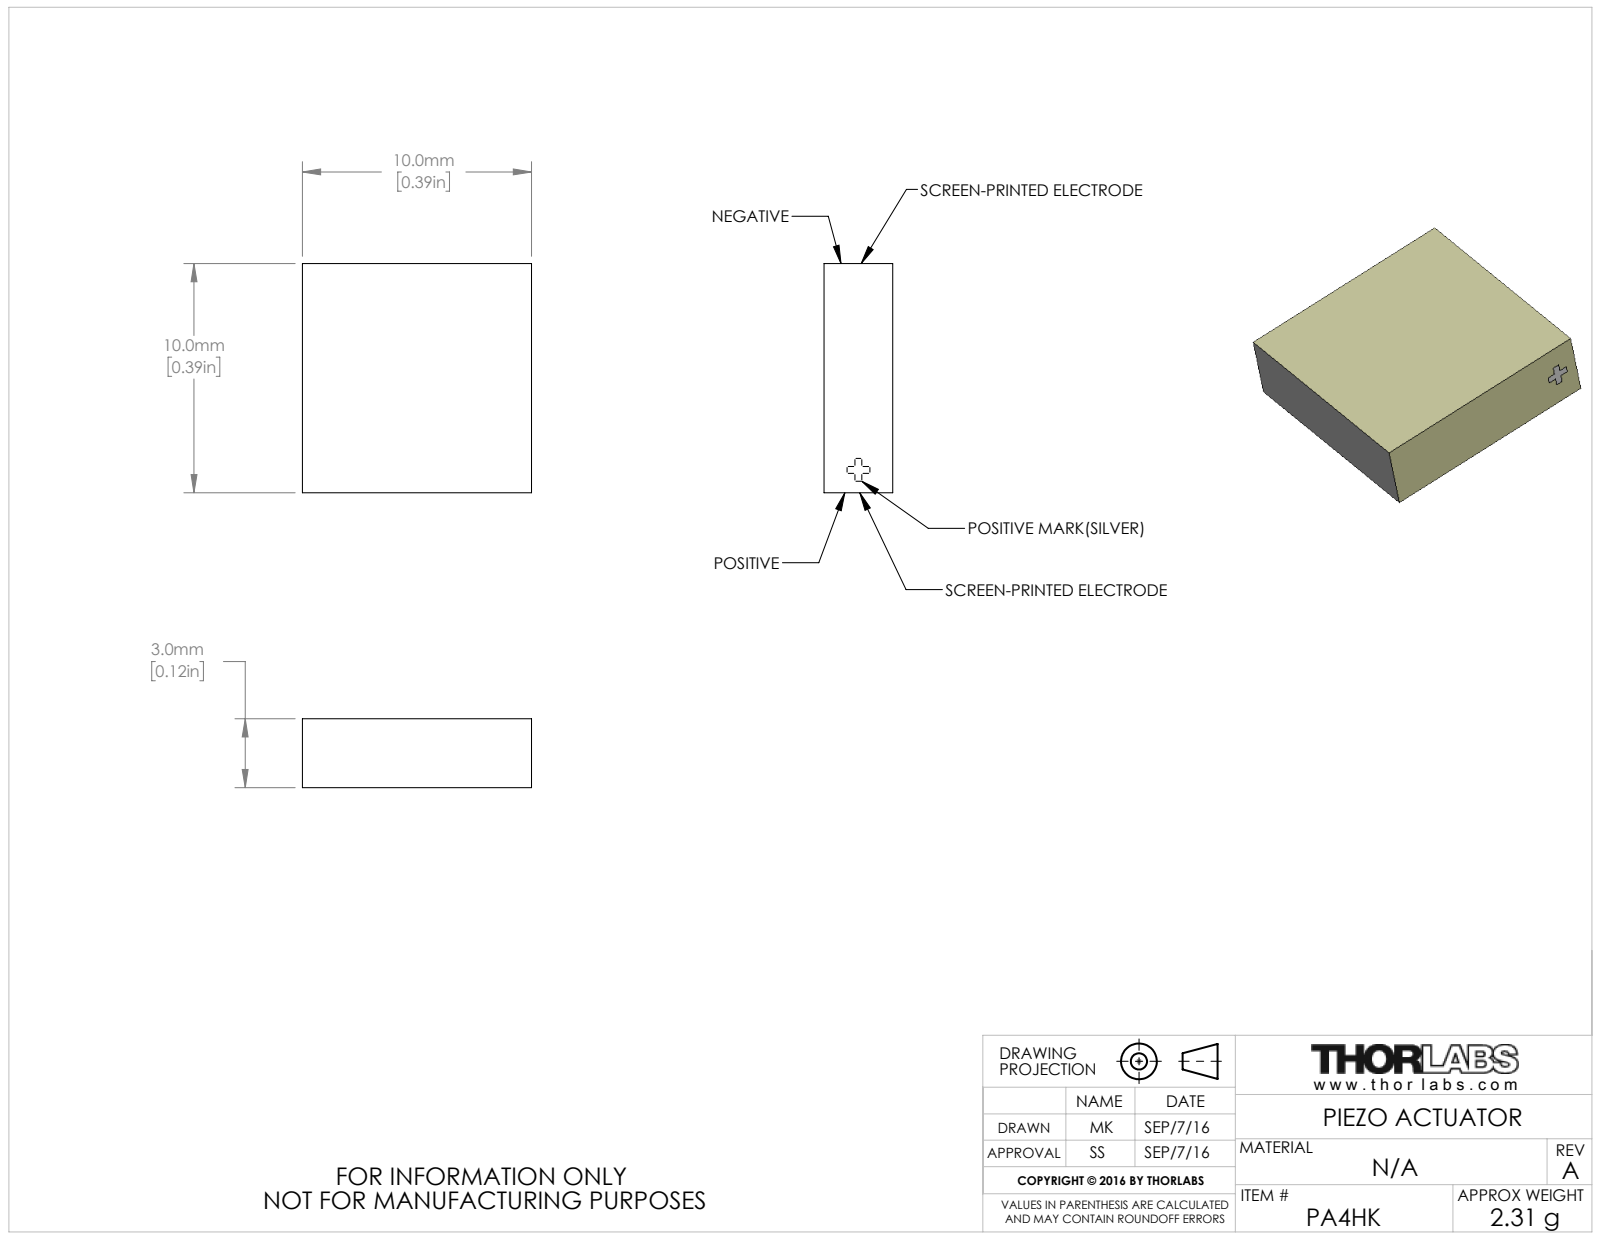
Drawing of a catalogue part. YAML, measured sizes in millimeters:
part_name: "CTN003179"
step_written_by: "SolidWorks 2016 (AUTOMOTIVE_DESIGN)"
units: millimeters
bodies: {solids: 1, faces: 7, planar: 7, cylindrical: 0, other: 0}
overall_size: [10, 10, 3]
volume: 300
surface_area: 320
face_to_face_distances: [3, 10]
